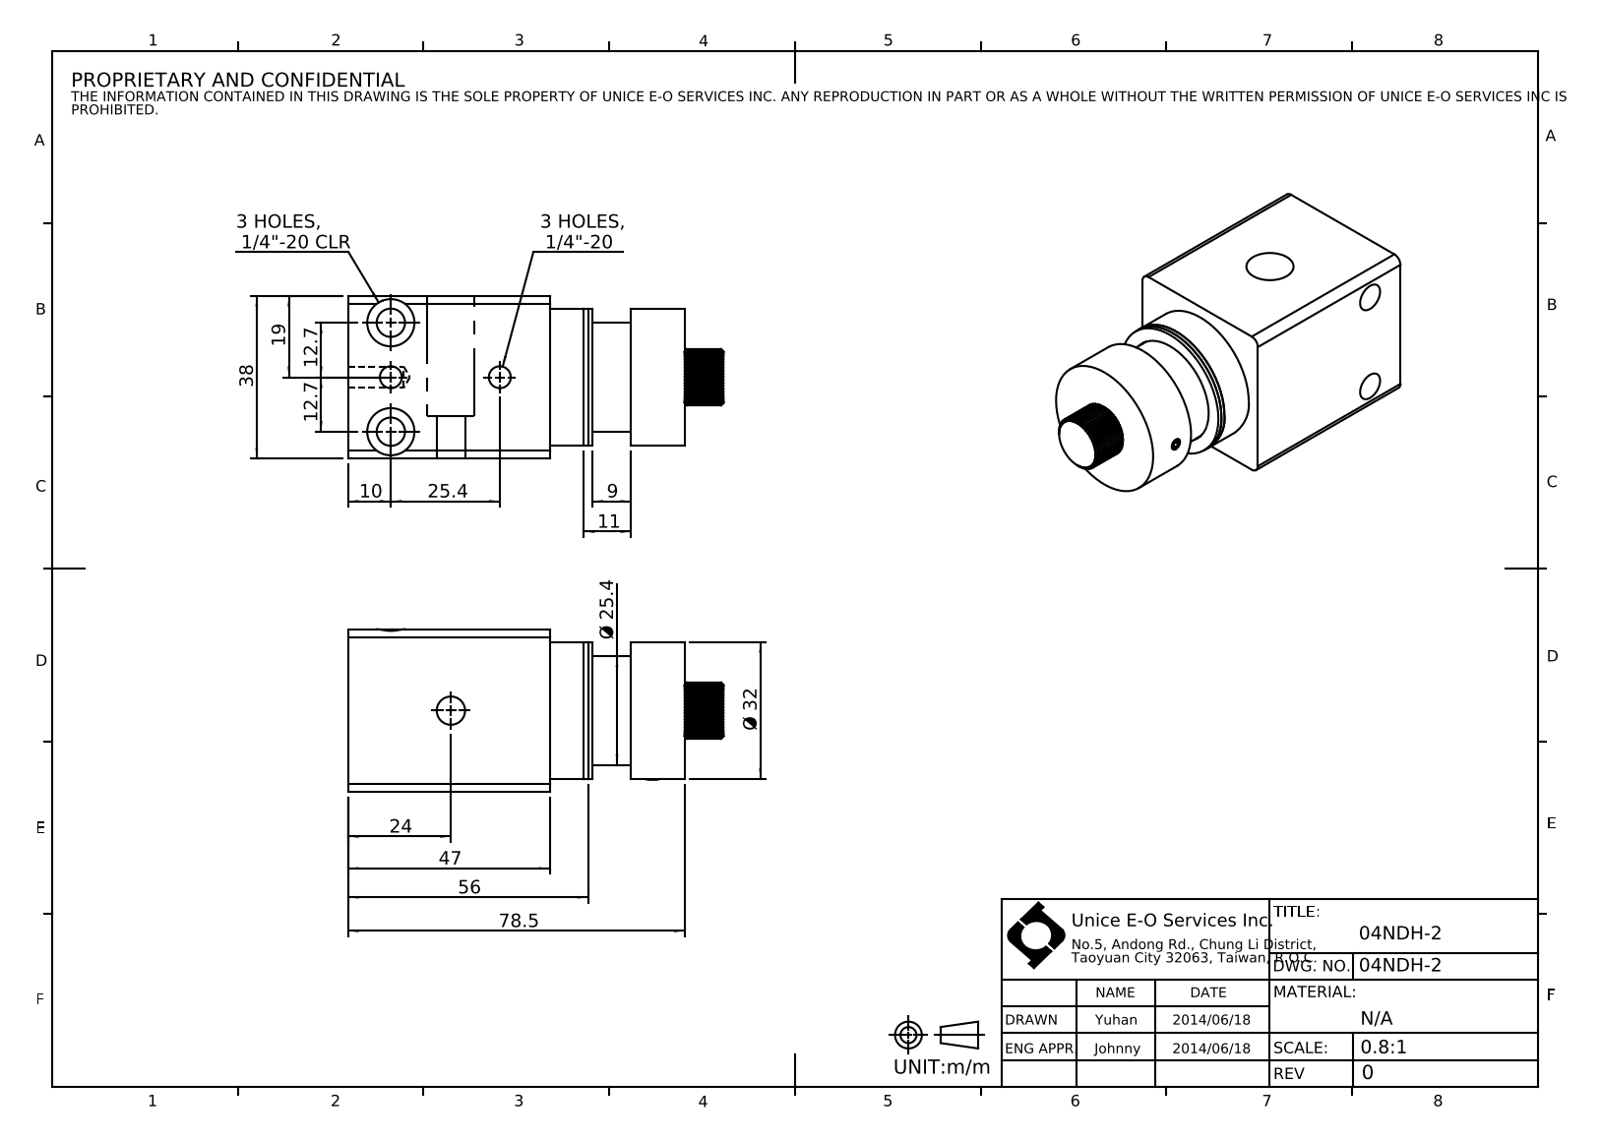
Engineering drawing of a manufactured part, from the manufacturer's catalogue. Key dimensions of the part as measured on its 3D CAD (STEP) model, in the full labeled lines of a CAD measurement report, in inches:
Part name (STEP PRODUCT): 04NDH-2
STEP written by: SolidWorks 2016 (CONFIG_CONTROL_DESIGN)
Units: inches
Bodies: 6 solids, 253 faces (133 planar, 100 cylindrical, 20 other)
Overall size (bounding box): 3.445 × 1.496 × 1.496
Volume: 4.973 in³ · Surface area: 35.29 in²
Round holes (diameter × count): ⌀0.26 ×3, ⌀0.433 ×3, ⌀0.201 ×2, ⌀0.098 ×1, ⌀0.197 ×1, ⌀0.256 ×1, ⌀1 ×1, ⌀1.008 ×1
Round bosses / shafts (diameter × count): ⌀1.26 ×1, ⌀0.236 ×1, ⌀0.118 ×1
Partial cylindrical surfaces — rounded edges, fillets, slot ends (radius × count): R0.079 ×4, R0.256 ×1
Main face-to-face distances: 1.496, 0.394, 0.354, 2.992, 0.039, 3.091, 0.098, 1.24, 1.85, 1.142
Hole centre spacings: 0.5, 1, 1.118
